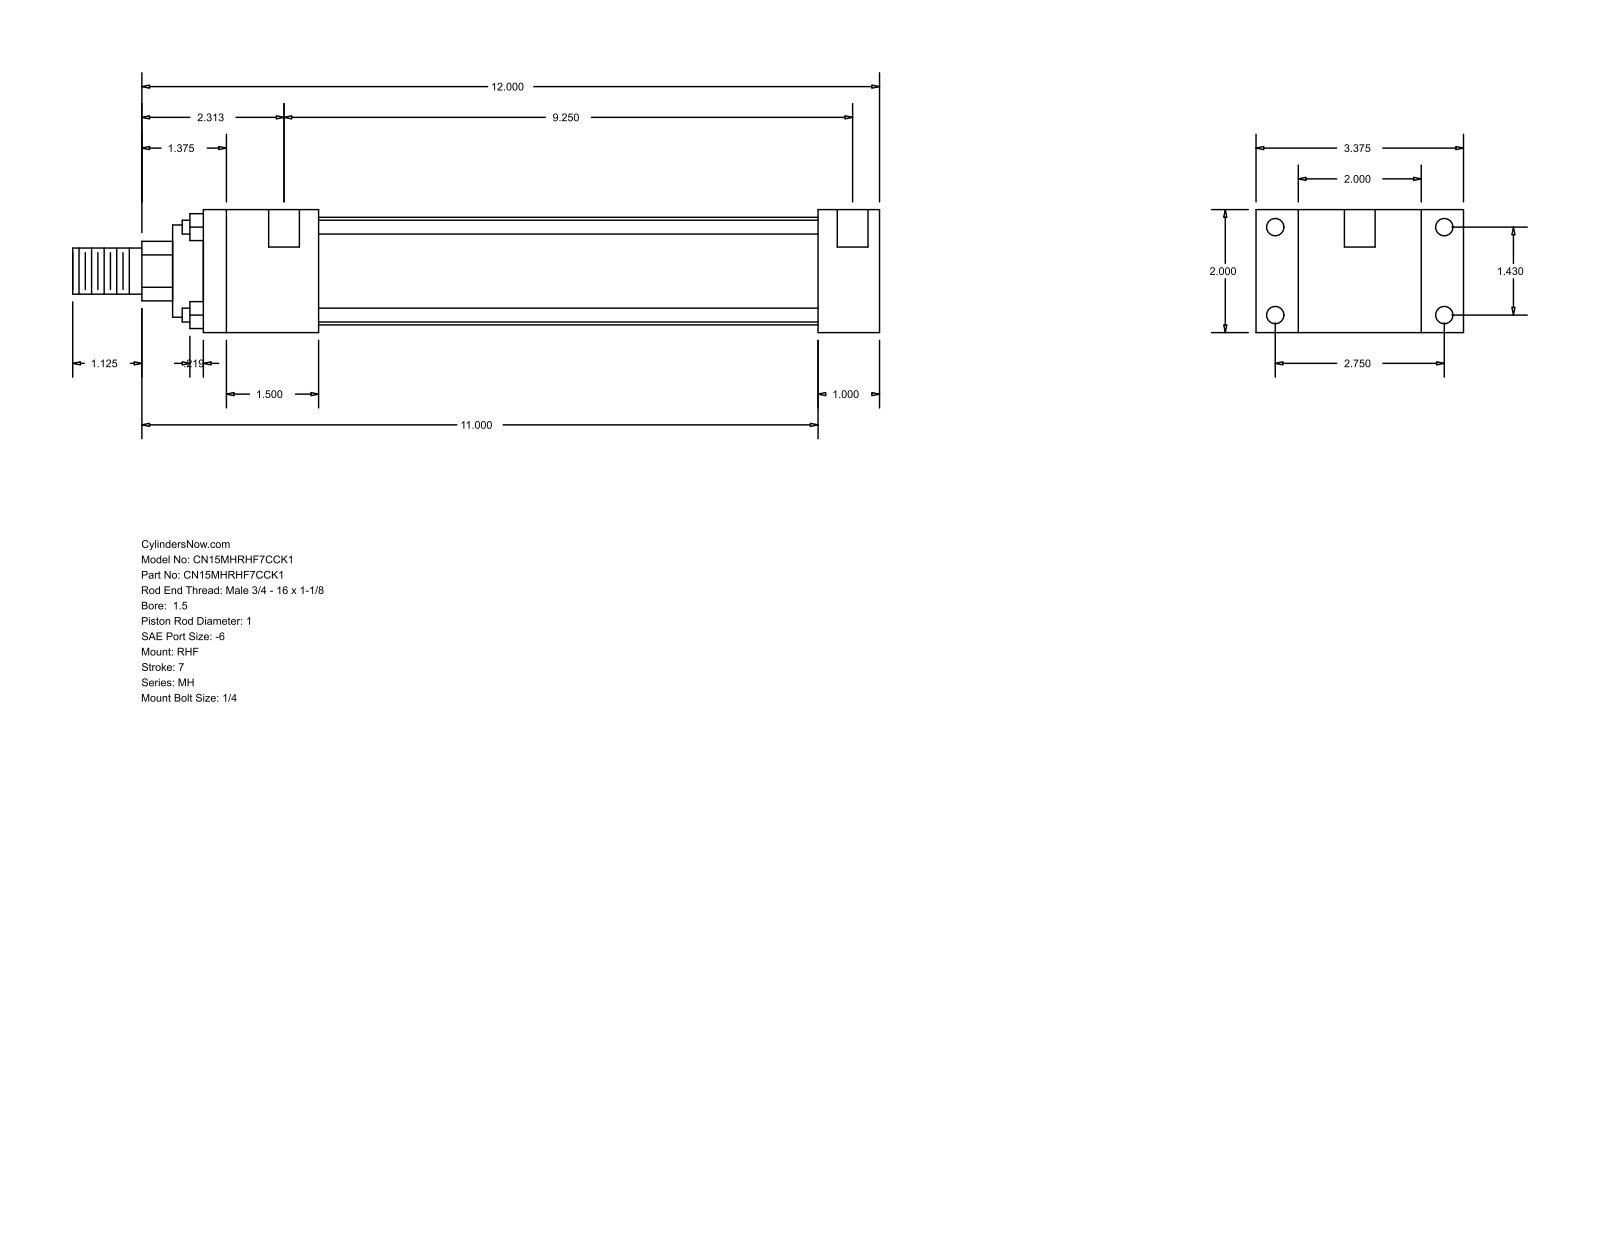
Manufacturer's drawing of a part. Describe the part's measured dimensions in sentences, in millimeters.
The part is named "MH_RHF__0150_1". Its 3-D file was written by "GSSL Pune (CONFIG_CONTROL_DESIGN)". It is 0 solids with 88 faces: 60 planar, 28 cylindrical and 0 other. Overall it measures 333.38 by 85.72 by 50.8 millimeters. Round holes: 4 of diameter 5.56, 4 of diameter 7.14, 2 of diameter 12.7. Round bosses or shafts: 4 of diameter 5.71, 1 of diameter 44.45, 1 of diameter 38.1, 1 of diameter 25.4, 1 of diameter 19.05. Partial cylindrical surfaces (rounded edges, fillets, slot ends): 1 of radius 12.29. The main face-to-face distances are 50.8, 25.4, 17.46, 68.26, 85.72, 279.4, 254, 47.63, 206.37, 231.77. The hole center spacings are 36.32, 69.84, 78.72, 238.13, 3.18, 234.95.
